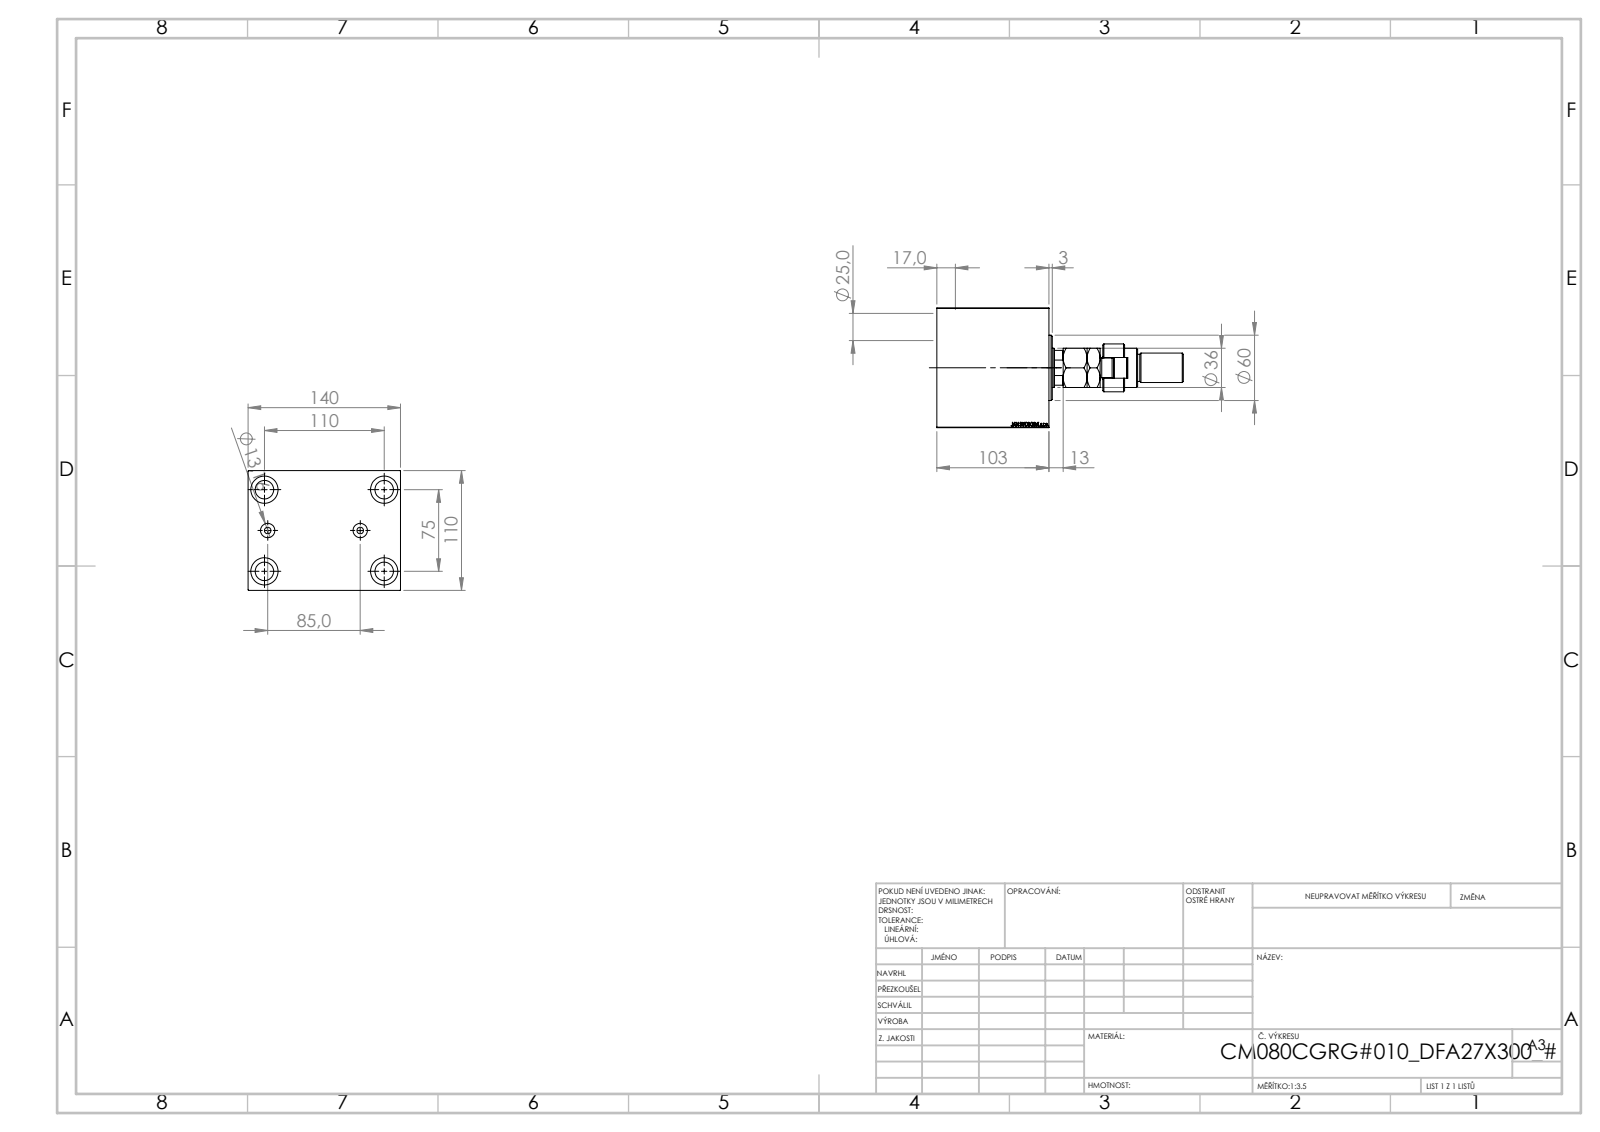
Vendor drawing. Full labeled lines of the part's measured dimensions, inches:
Part name (STEP PRODUCT): V450CM_C_VCP; MFA; FEMALE_PART_FOR_DFA; V450CM_C_Body (+1 more)
STEP written by: SolidWorks 2019 (CONFIG_CONTROL_DESIGN)
Units: inches
Bodies: 5 solids, 948 faces (439 planar, 71 cylindrical, 438 other)
Overall size (bounding box): 8.957 × 5.512 × 4.331
Volume: 92.02 in³ · Surface area: 279.9 in²
Round holes (diameter × count): ⌀0.669 ×4, ⌀0.984 ×4, ⌀0.236 ×2, ⌀0.518 ×2, ⌀1.004 ×1, ⌀1.555 ×1, ⌀3.15 ×1, ⌀3.228 ×1, ⌀3.425 ×1
Round bosses / shafts (diameter × count): ⌀2.362 ×1, ⌀1.732 ×1, ⌀1.417 ×1, ⌀1.102 ×1, ⌀1.063 ×1, ⌀0.984 ×1, ⌀0.709 ×1
Partial cylindrical surfaces — rounded edges, fillets, slot ends (radius × count): R0.374 ×1, R0.591 ×1, R0.689 ×1
Main face-to-face distances: 4.331, 5.512, 4.055, 1.9, 2.156, 0.394, 0.787, 3.661, 3.268, 1.506
Hole centre spacings: 1.556, 2.621, 4.113, 1.673, 2.953, 4.331, 5.242, 3.346
